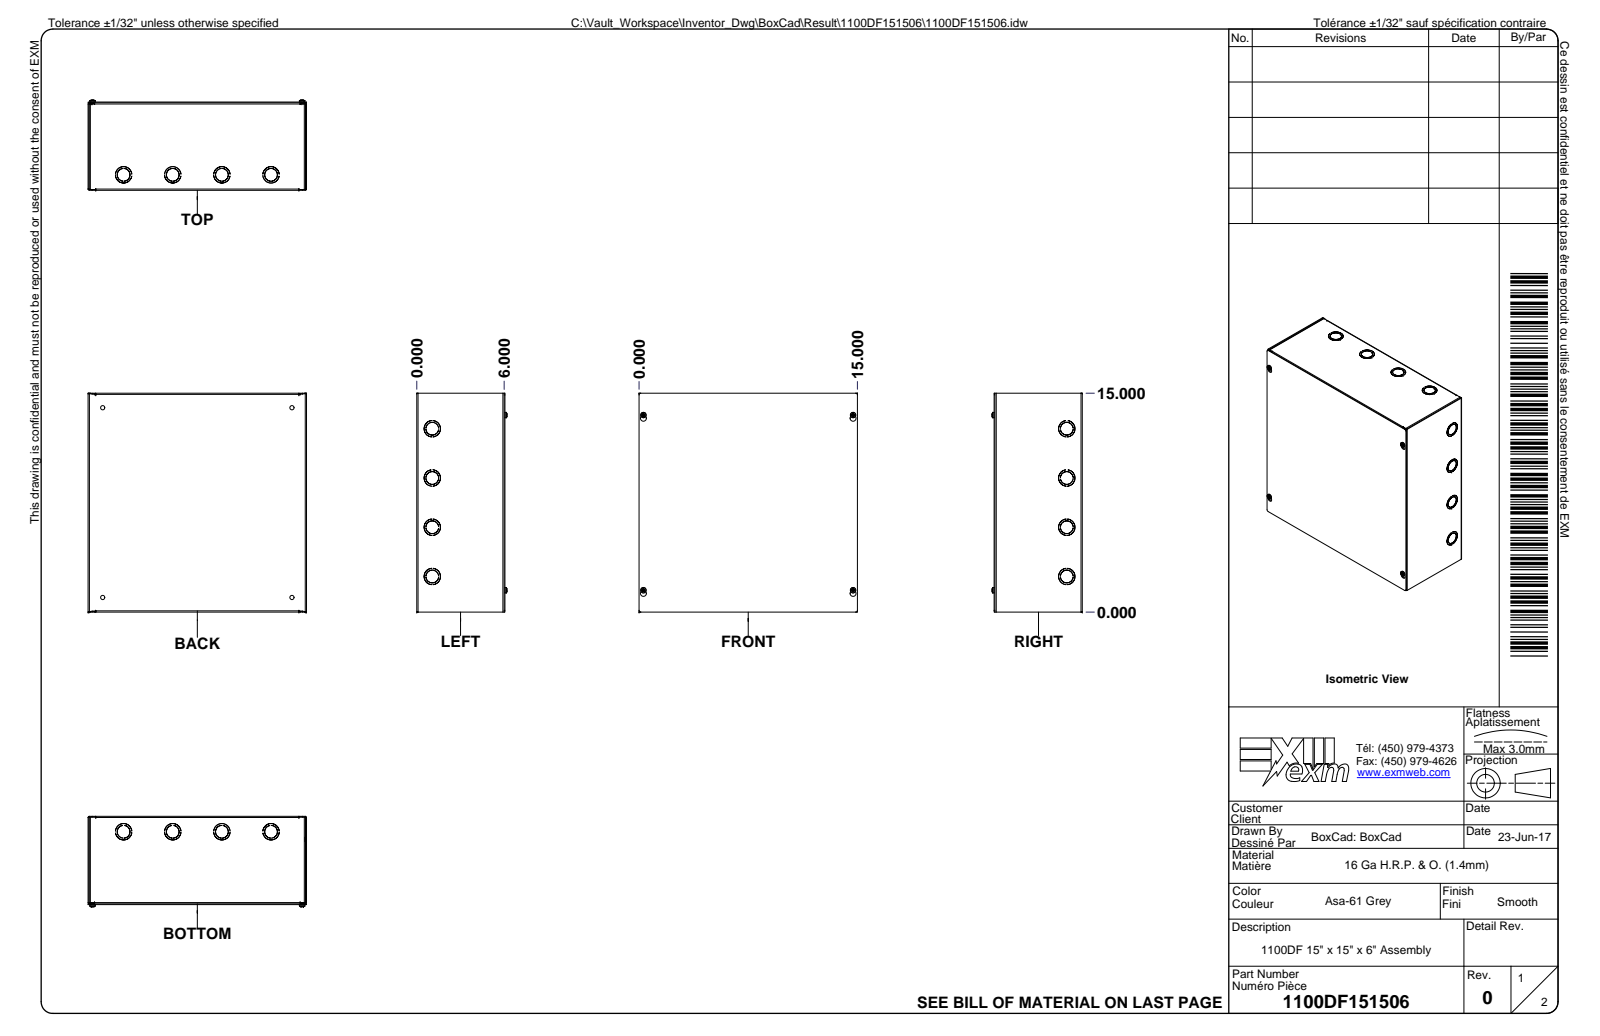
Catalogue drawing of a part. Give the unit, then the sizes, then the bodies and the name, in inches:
Units: inches
Overall size (bounding box): 15 × 15 × 6.183
Round holes (diameter × count): ⌀0.165 ×8, ⌀0.875 ×8, ⌀1.125 ×8, ⌀0.29 ×4, ⌀0.406 ×4, ⌀0.033 ×2, ⌀0.177 ×2, ⌀0.043 ×1, ⌀0.312 ×1, ⌀1.063 ×1
Round bosses / shafts (diameter × count): ⌀1.125 ×8, ⌀0.875 ×8, ⌀0.374 ×4, ⌀0.03 ×2, ⌀1.25 ×1, ⌀1.142 ×1, ⌀0.25 ×1, ⌀0.051 ×1
Partial cylindrical surfaces — rounded edges, fillets, slot ends (radius × count): R0.004 ×28, R0.031 ×14, R0.086 ×14, R0.059 ×12, R0.11 ×12, R0.062 ×4, R0.094 ×4, R0.117 ×4
Main face-to-face distances: 0.055, 14.945, 5.945, 0.053, 6, 6.053, 5.998, 15, 14.89, 5.89
Hole centre spacings: 0.86, 12.52, 13.254, 13.709, 18.546, 12, 14.4, 18.744
Volume: 45.75 in³ · Surface area: 1 705 in²
Bodies: 8 solids, 3521 faces (2146 planar, 483 cylindrical, 892 other)
Part name (STEP PRODUCT): 1100DF151506; 1100DF151506B; 1100DF151506B-P; 1100DF151506C (+5 more)
STEP written by: Autodesk Inventor 2024 (AUTOMOTIVE_DESIGN)
